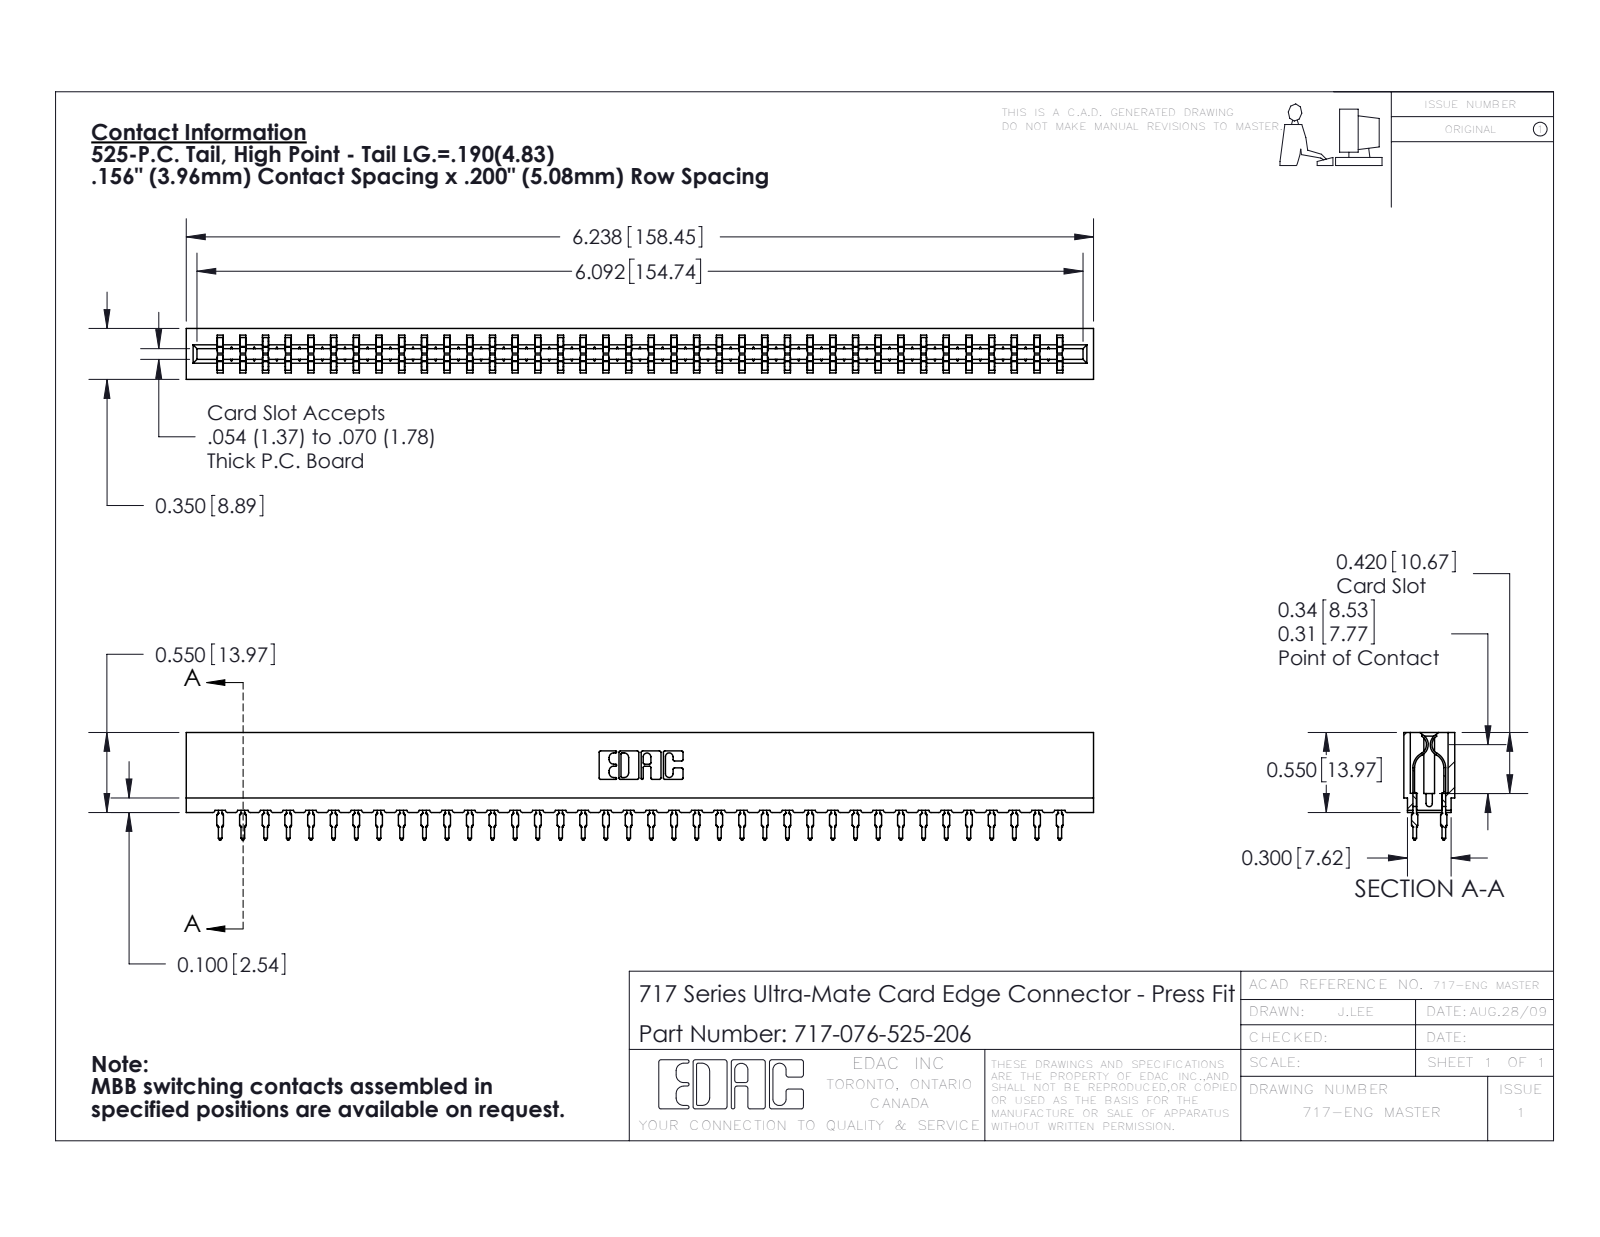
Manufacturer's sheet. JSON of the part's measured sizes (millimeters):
{"part_name": "717 Part_Insulator Option - 06; 745-292-001_525; 717-076-525-206", "step_written_by": "SolidWorks 2016 (CONFIG_CONTROL_DESIGN)", "units": "millimeters", "bodies": {"solids": 77, "faces": 6934, "planar": 3588, "cylindrical": 1370, "other": 1976}, "overall_size": [158.4, 18.8, 8.9], "volume_mm3": 13700, "surface_area_mm2": 20860, "partial_cylinders_radius": [[0.5, 152], [0.4, 76], [0.3, 22], [0.1, 8], [0.3, 8], [0.2, 6], [0.8, 6], [0.7, 3]], "face_to_face_distances": [5.4, 3.5, 8.9, 1.6, 7.3, 1.9, 3.8, 1.9, 1.1, 7.7]}
